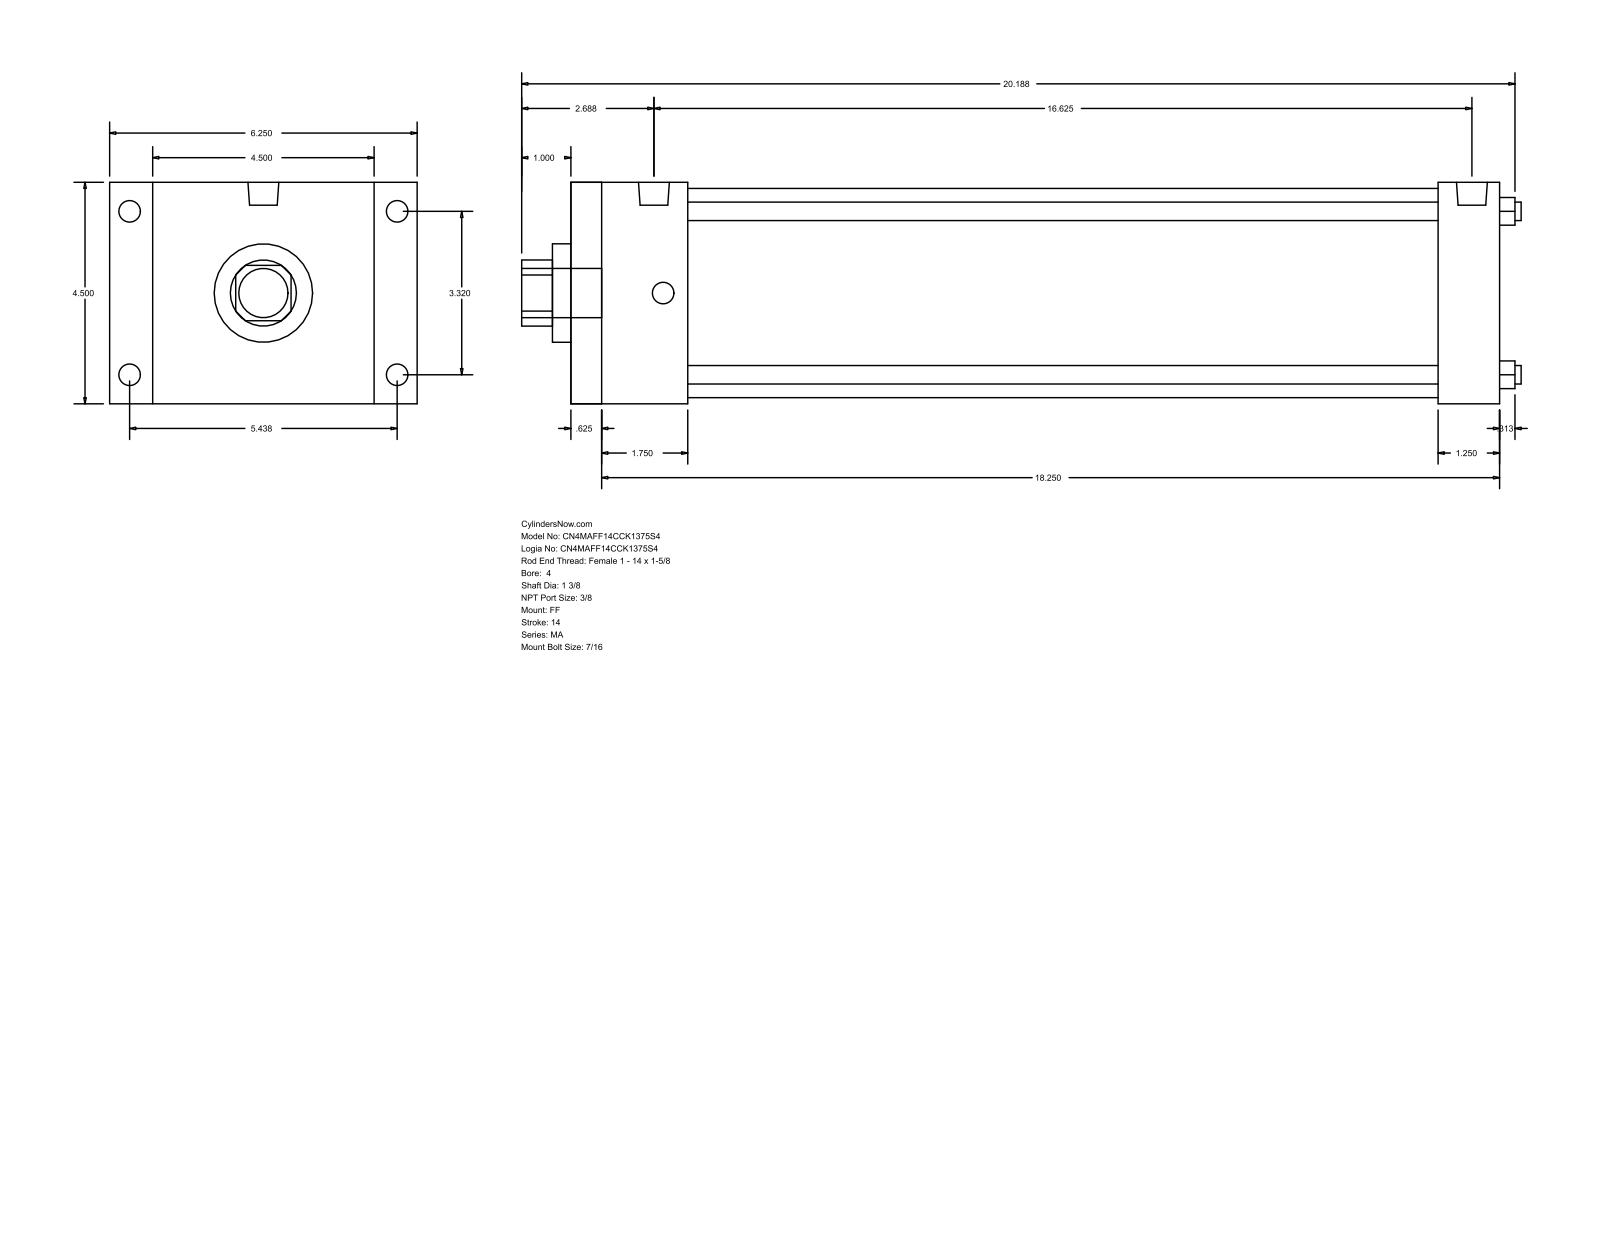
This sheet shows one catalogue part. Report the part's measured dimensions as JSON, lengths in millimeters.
{"part_name": "MA_FF__0400_1.375", "step_written_by": "GSSL Pune (CONFIG_CONTROL_DESIGN)", "units": "millimeters", "bodies": {"solids": 0, "faces": 92, "planar": 64, "cylindrical": 28, "other": 0}, "overall_size": [515.94, 158.75, 114.3], "round_holes": [[9.53, 4], [34.92, 1], [50.8, 1], [107.95, 1]], "round_bosses_or_shafts": [[11.11, 8], [15.93, 2], [25.4, 1]], "partial_cylinders_radius": [[17.06, 1]], "face_to_face_distances": [114.3, 479.42, 15.87, 463.55, 22.23, 136.53, 447.67, 431.8, 31.75, 60.32], "hole_center_spacings": [59.62, 84.32, 119.25]}
